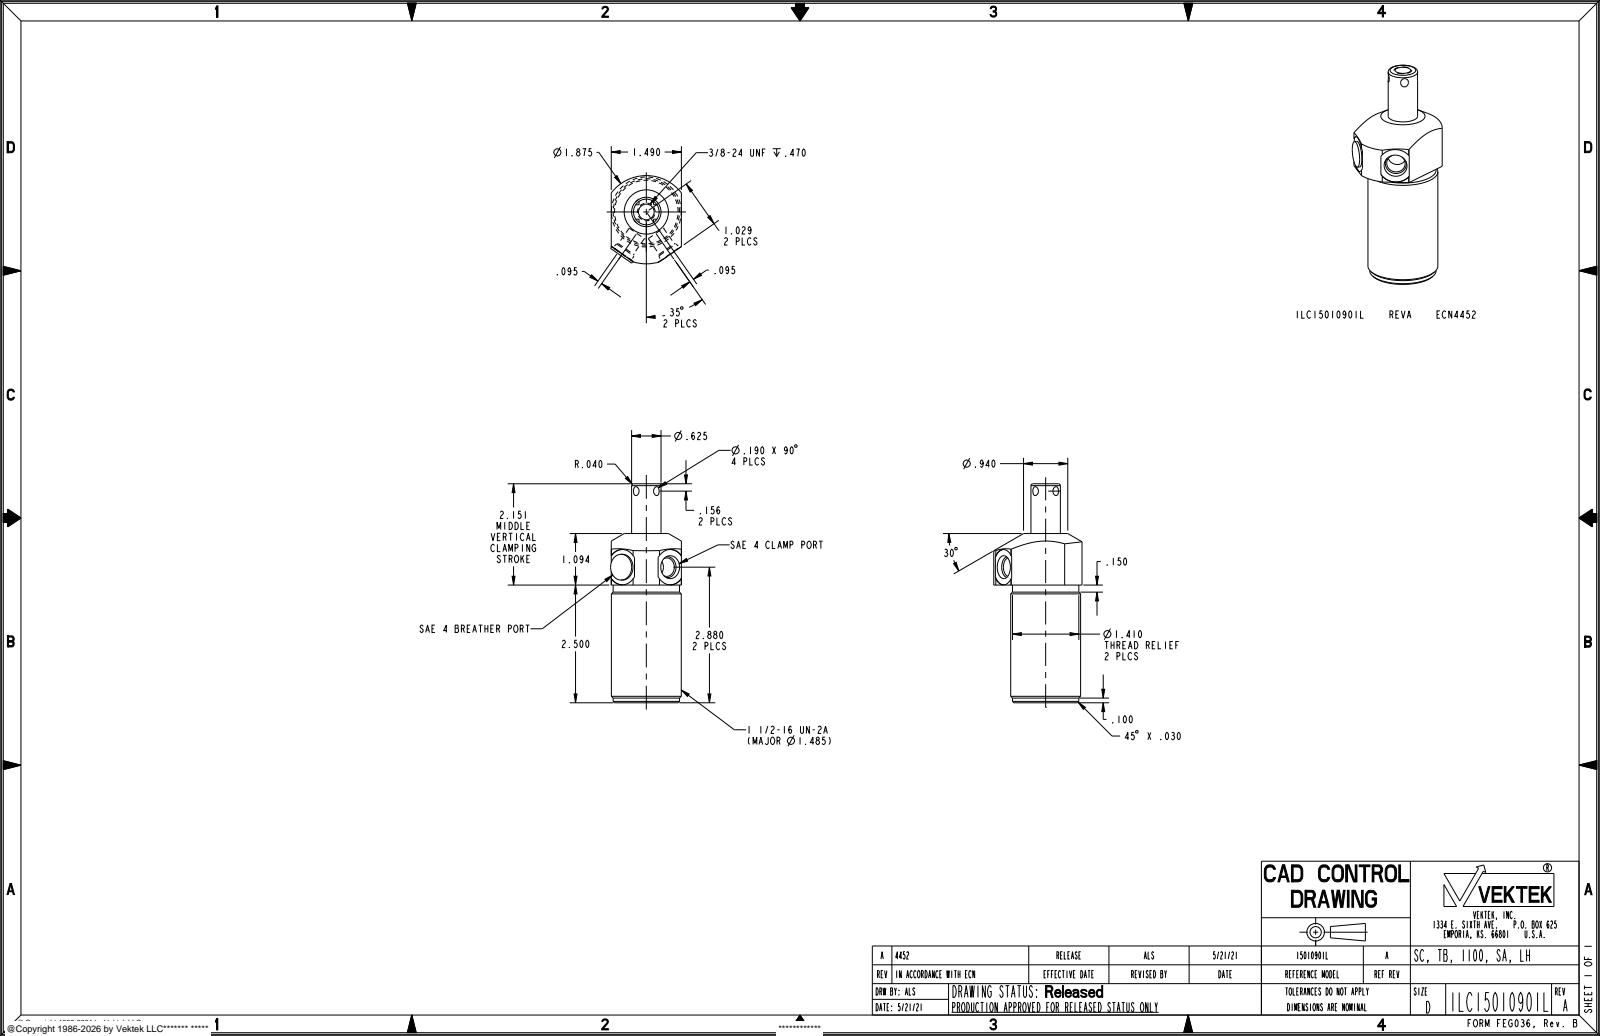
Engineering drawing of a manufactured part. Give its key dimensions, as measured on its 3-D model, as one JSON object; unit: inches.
{"part_name": "ILC15010901L", "step_written_by": "PRO/ENGINEER BY PARAMETRIC TECHNOLOGY CORPORATION, 2013320 (CONFIG_CONTROL_DESIGN)", "units": "inches", "bodies": {"solids": 1, "faces": 73, "planar": 17, "cylindrical": 28, "other": 28}, "overall_size": [4.651, 1.875, 1.504], "volume_in3": 6.816, "surface_area_in2": 26.68, "round_holes": [[0.392, 2], [0.332, 1]], "round_bosses_or_shafts": [[1.485, 1], [1.41, 1], [0.625, 1], [0.547, 1], [0.375, 1]], "partial_cylinders_radius": [[0.375, 2], [0.937, 1]], "face_to_face_distances": [1.49, 2.5, 3.594, 1.094, 0.53, 0.05, 4.651, 2.151, 1.057, 0.58]}
